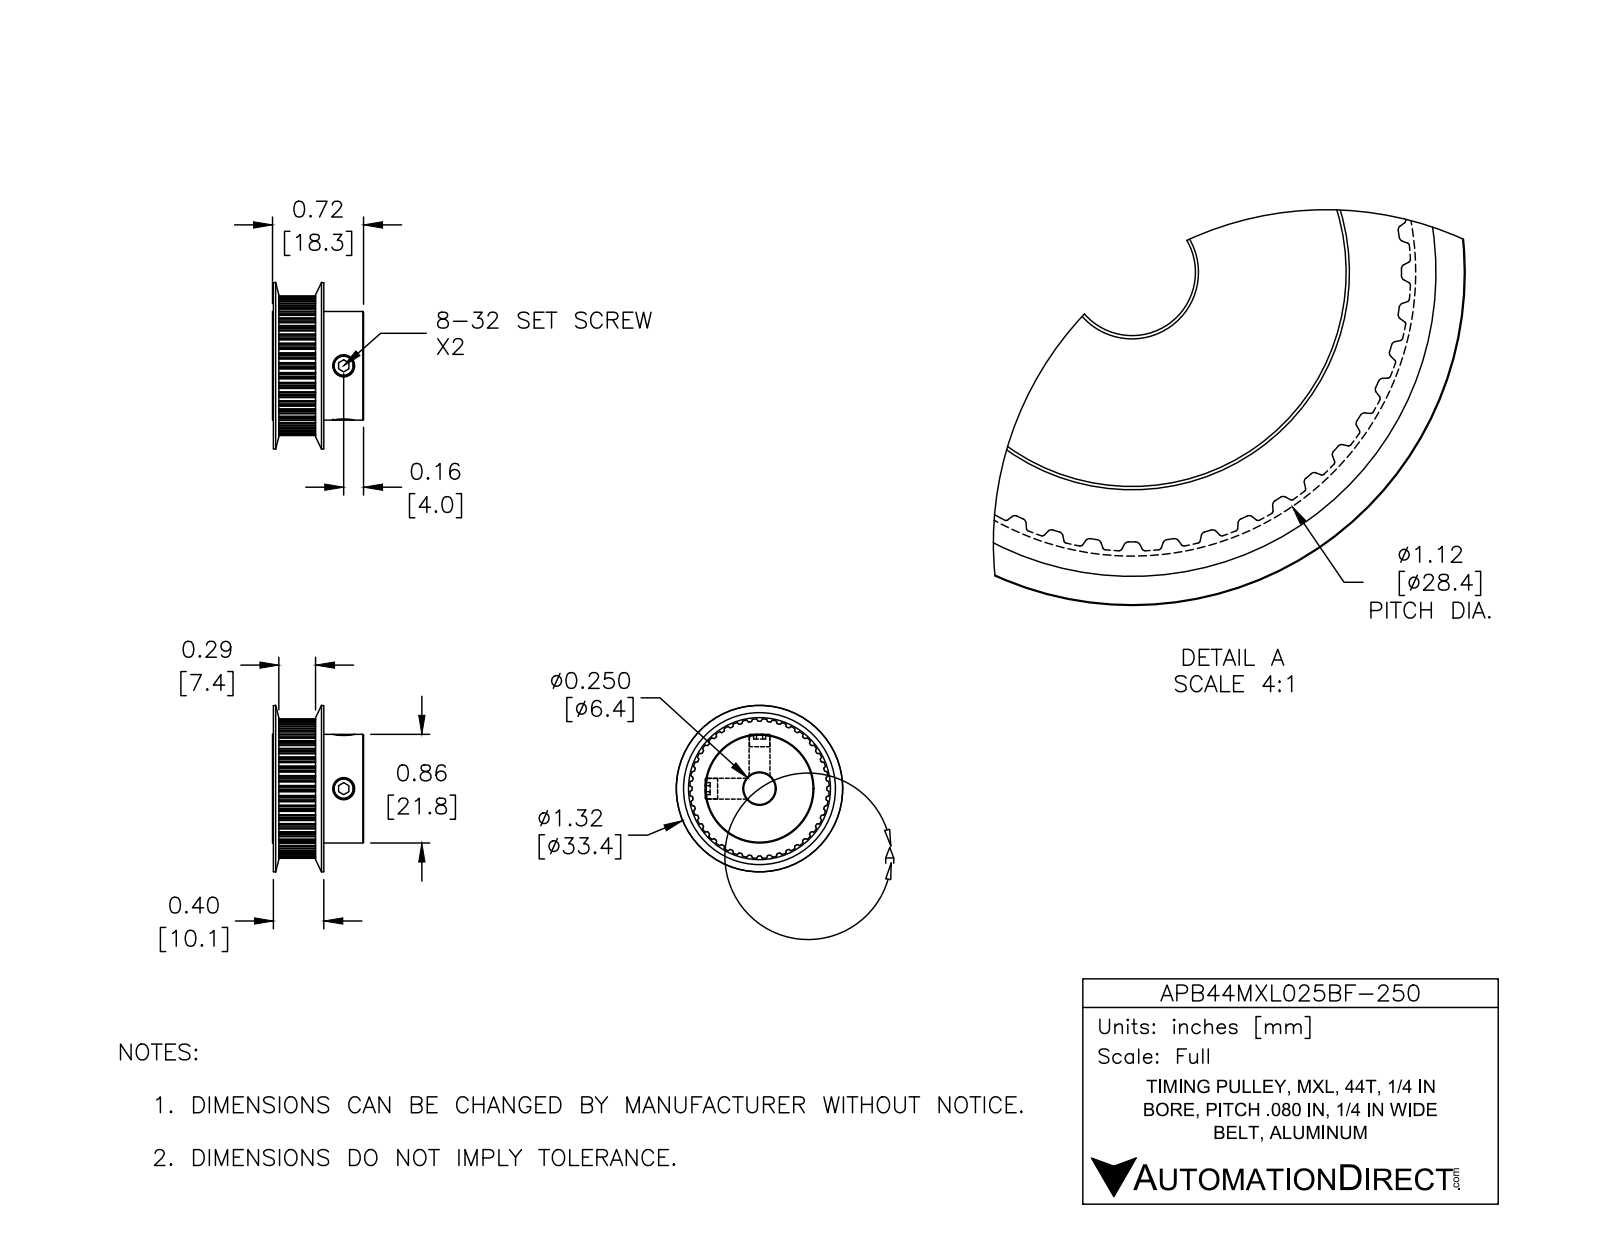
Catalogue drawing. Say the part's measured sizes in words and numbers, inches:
The part is named "APB44MXL025BF-250". Its 3-D file was written by "SolidWorks 2016 (AUTOMOTIVE_DESIGN)". It is 3 solids with 449 faces: 112 planar, 311 cylindrical and 26 other. Overall it measures 1.315 by 1.315 by 0.719 inches. Its volume is 0.517 cubic inches and its surface area 6.869 square inches. Round holes: 2 of diameter 0.164, 1 of diameter 0.25. Round bosses or shafts: 2 of diameter 0.16, 1 of diameter 0.858. Partial cylindrical surfaces (rounded edges, fillets, slot ends): 88 of radius 0.005, 88 of radius 0.009, 1 of radius 0.532, 1 of radius 0.55. The main face-to-face distances are 0.362, 0.025, 0.387, 0.719, 0.694, 0.332, 0.477, 0.05, 0.025, 0.337.
